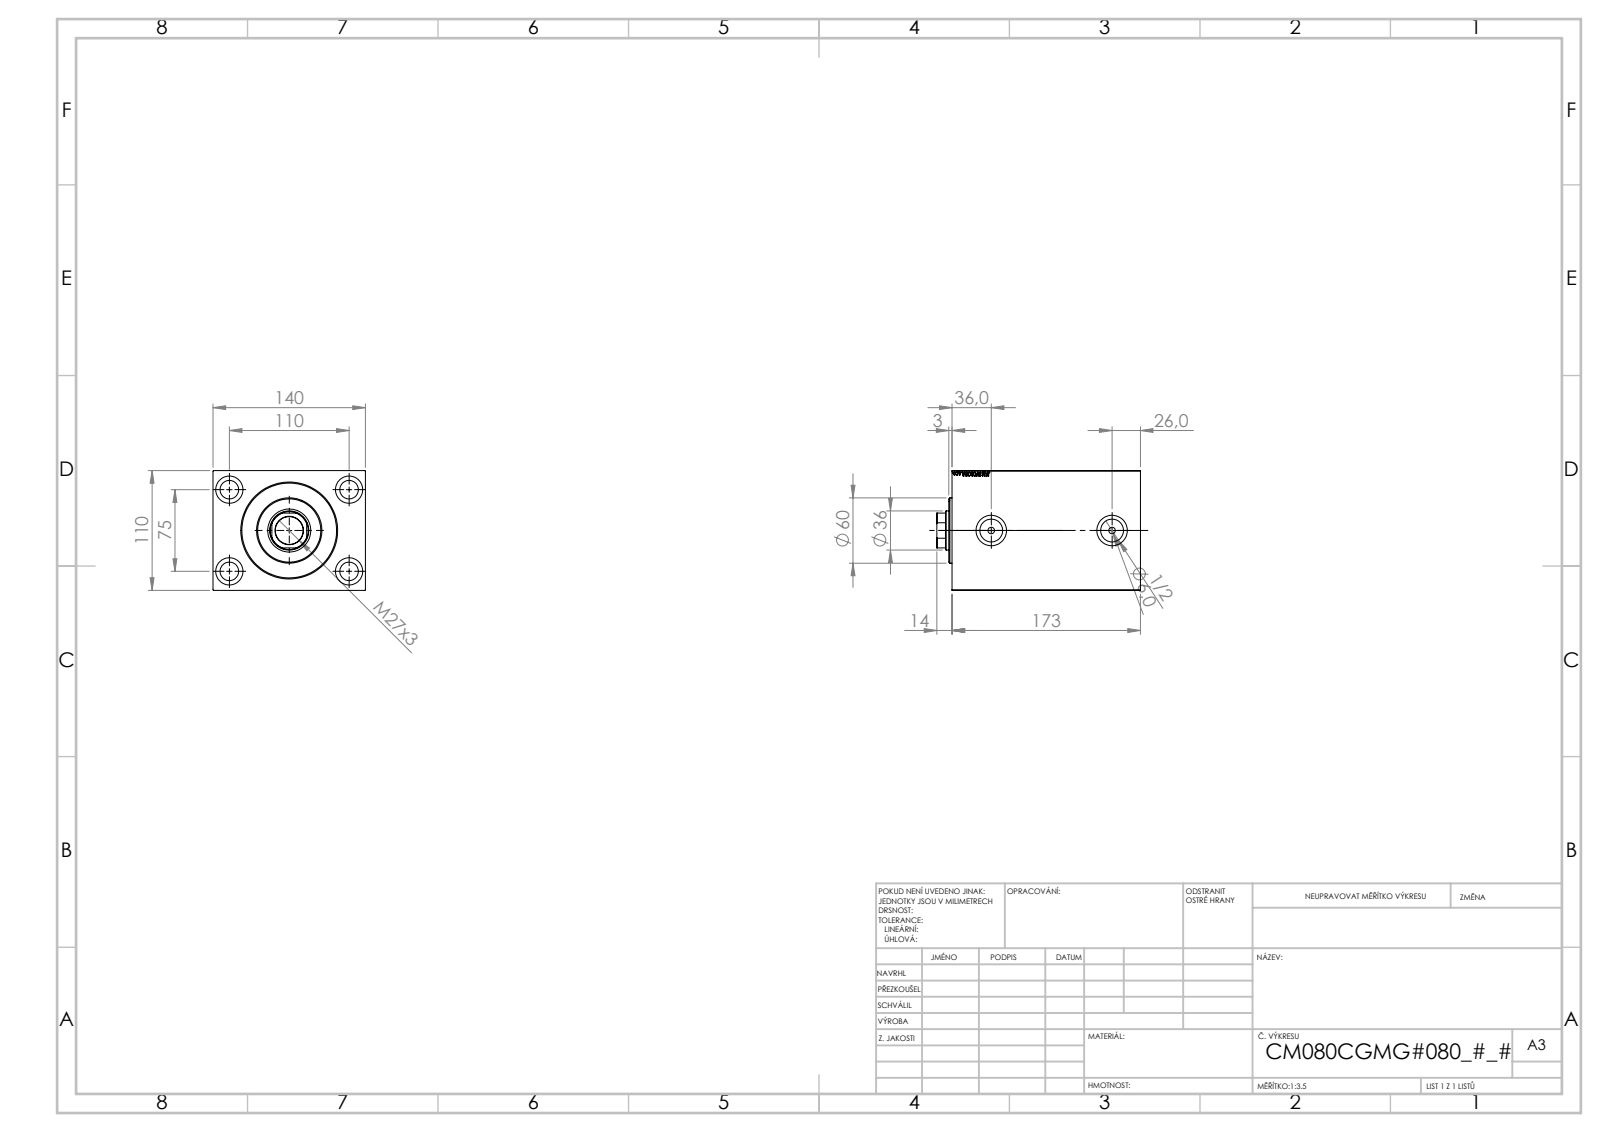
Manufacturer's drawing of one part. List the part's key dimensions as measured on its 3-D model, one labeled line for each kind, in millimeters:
Part name (STEP PRODUCT): V450CM_C_VCP; V450CM_C_Body; V450CM_VC_B
STEP written by: SolidWorks 2019 (CONFIG_CONTROL_DESIGN)
Units: millimetres
Bodies: 3 solids, 865 faces (409 planar, 62 cylindrical, 394 other)
Overall size (bounding box): 187 × 140 × 110
Volume: 2 141 000 mm³ · Surface area: 257 162 mm²
Round holes (diameter × count): ⌀17 ×4, ⌀25 ×4, ⌀6 ×2, ⌀20.96 ×2, ⌀28 ×2, ⌀25.5 ×1, ⌀36 ×1, ⌀39.5 ×1, ⌀80 ×1, ⌀82 ×1, ⌀87 ×1
Round bosses / shafts (diameter × count): ⌀60 ×1
Partial cylindrical surfaces — rounded edges, fillets, slot ends (radius × count): R17.5 ×1
Main face-to-face distances: 110, 140, 173, 152, 21, 37.3, 114.7, 135.7, 117.3, 80
Hole centre spacings: 66.57, 75, 110, 133.14, 111
